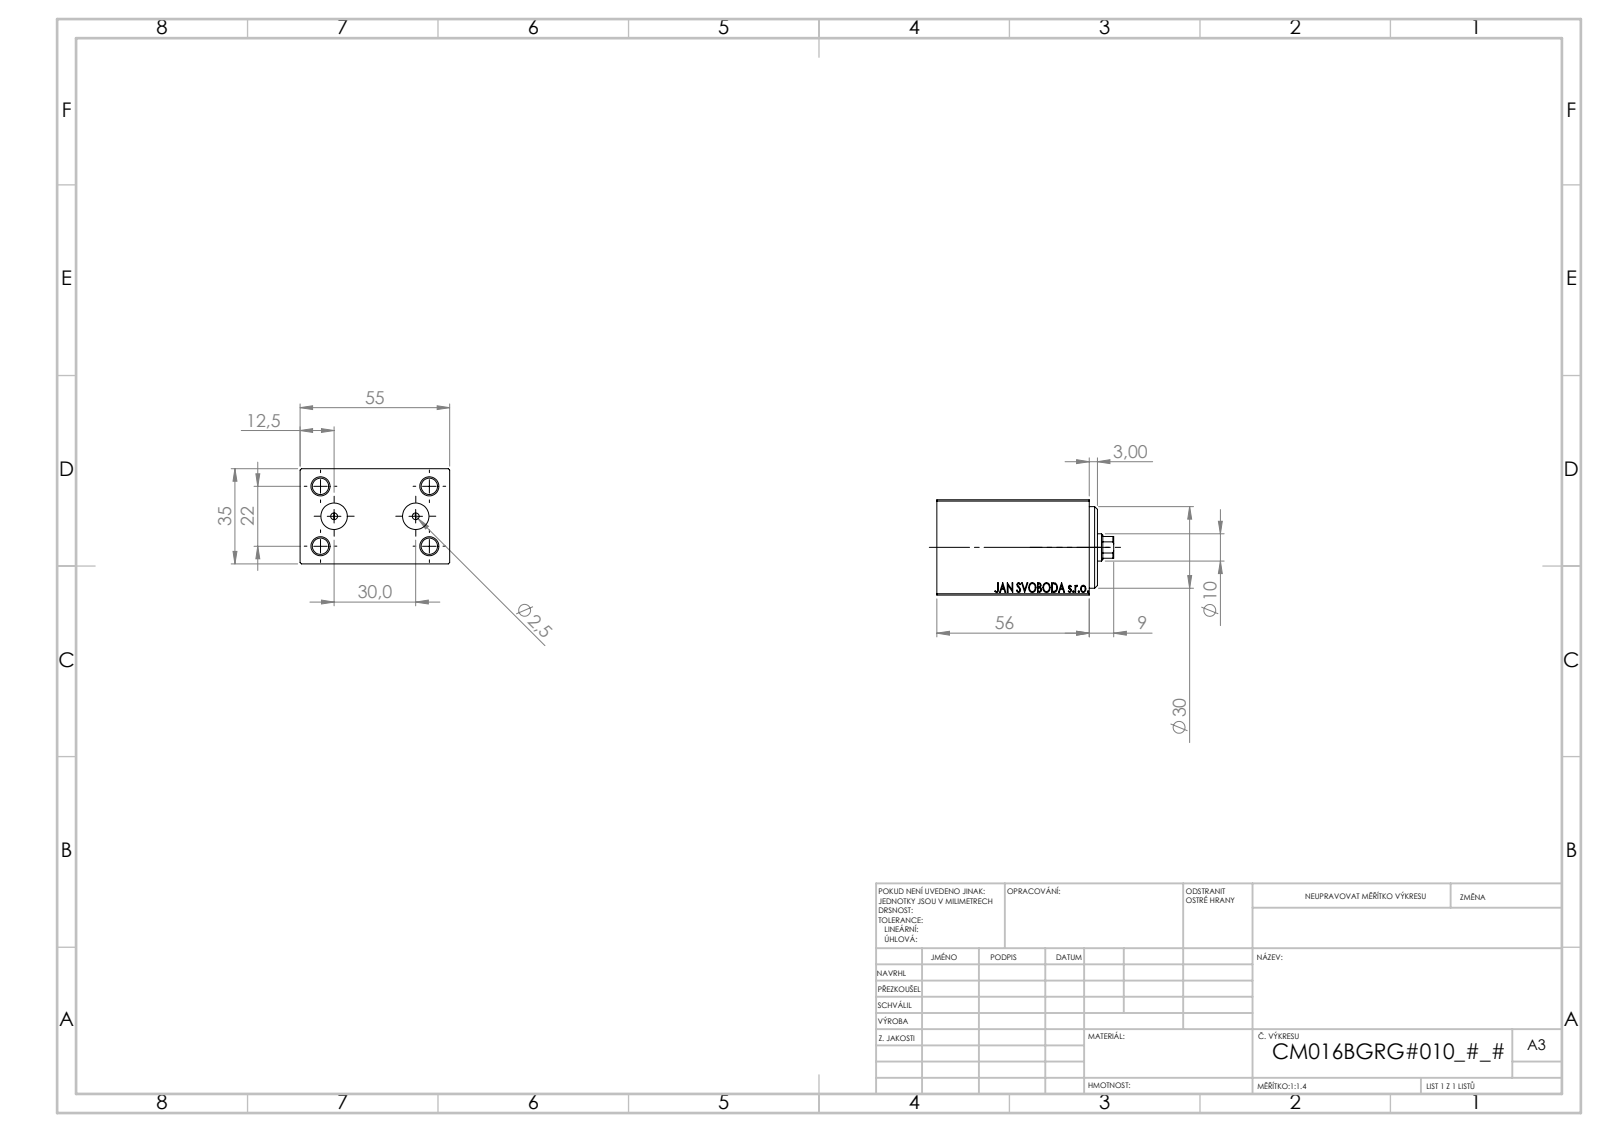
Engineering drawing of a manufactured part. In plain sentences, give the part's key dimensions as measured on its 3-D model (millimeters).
The part is named "V450CM_VC_B; V450CM_B_VCP; V450CM_B_Body". Its 3-D file was written by "SolidWorks 2019 (CONFIG_CONTROL_DESIGN)". It is 3 solids with 877 faces: 401 planar, 50 cylindrical and 426 other. Overall it measures 65 by 55 by 35 millimeters. Its volume is 104 341 cubic millimeters and its surface area 25 113 square millimeters. Round holes: 4 of diameter 6, 2 of diameter 2.5, 2 of diameter 9.72, 1 of diameter 4.5, 1 of diameter 10, 1 of diameter 13.5, 1 of diameter 14.5, 1 of diameter 16, 1 of diameter 18, 1 of diameter 30. Partial cylindrical surfaces (rounded edges, fillets, slot ends): 1 of radius 4.5. The main face-to-face distances are 35, 55, 5, 51, 56, 46, 8, 3, 59, 54. The hole center spacings are 12.08, 22.83, 36.69, 15, 22, 40, 45.65, 30.
